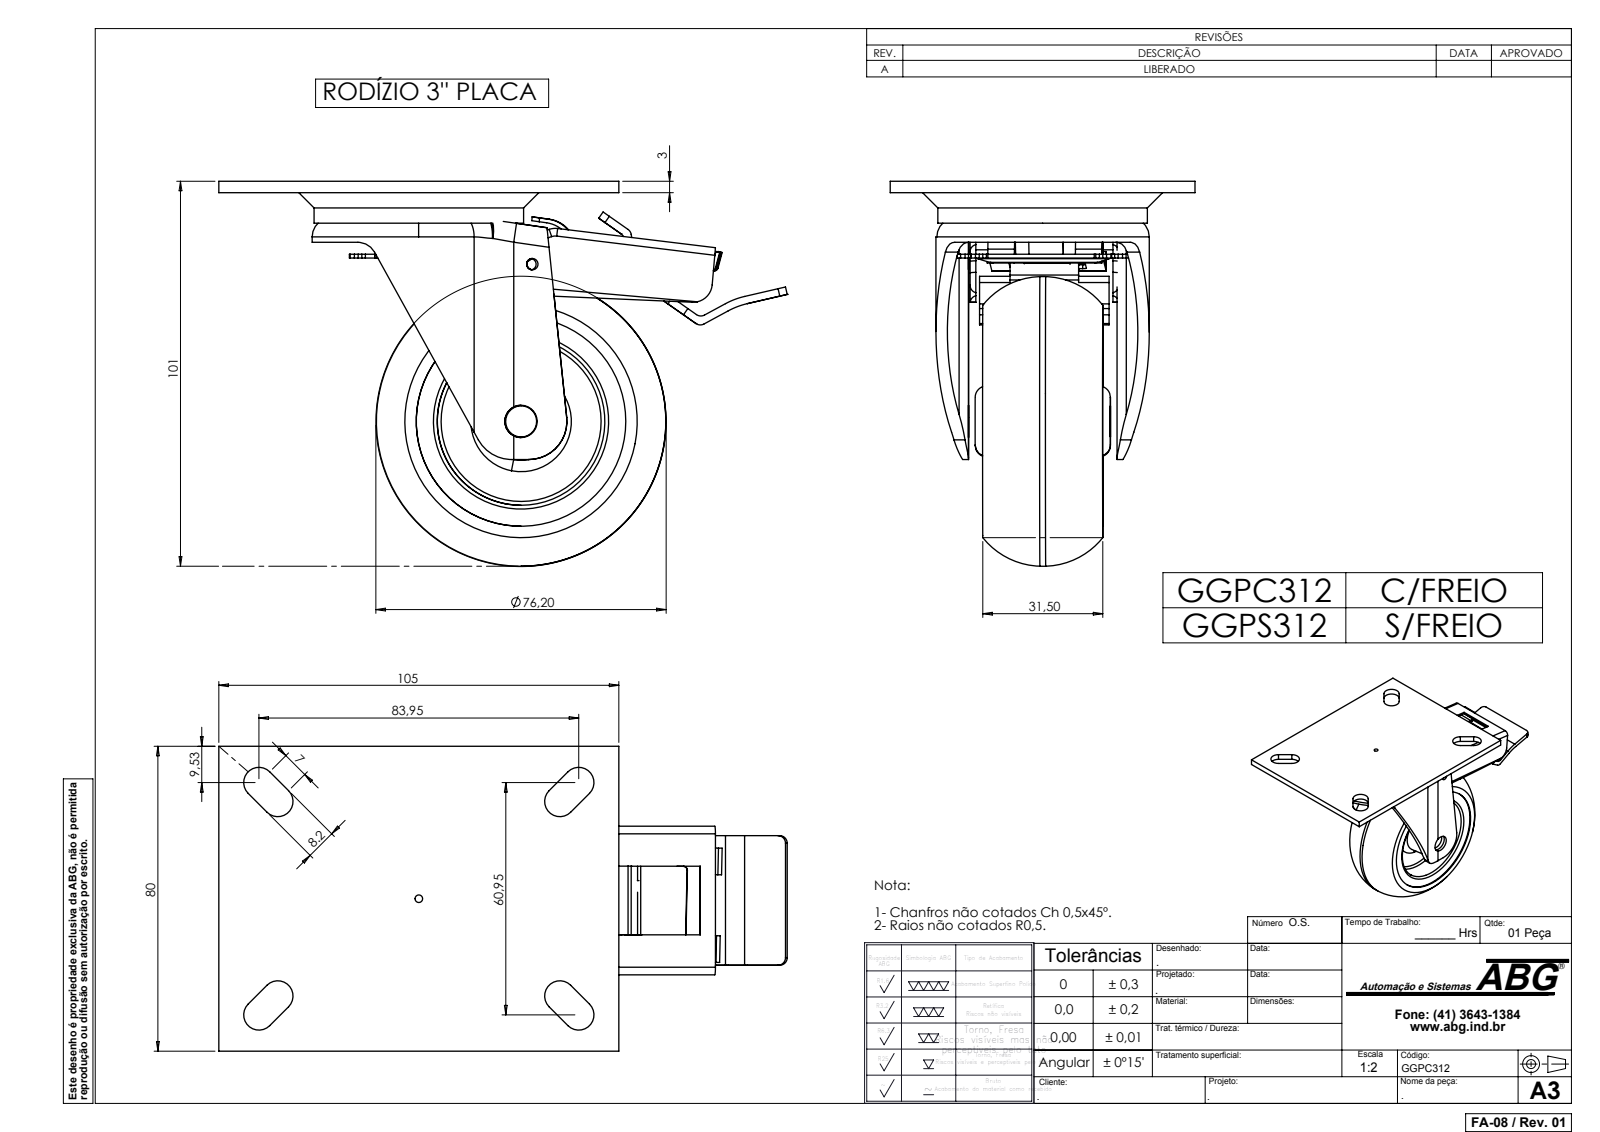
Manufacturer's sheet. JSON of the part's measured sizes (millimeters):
{"part_name": "ROD 3'''''''' -1; ROD 3'''''''' -3-1; GGPCF312; ROD 3''''''''-4 (+3 more)", "step_written_by": "SolidWorks 2007 (CONFIG_CONTROL_DESIGN)", "units": "millimeters", "bodies": {"solids": 6, "faces": 371, "planar": 152, "cylindrical": 176, "other": 43}, "overall_size": [149.2, 101.01, 80], "volume_mm3": 162965, "surface_area_mm2": 65323, "round_holes": [[3, 2], [8.5, 2], [44, 2], [55, 2], [2, 1], [8.2, 1], [25, 1], [50, 1]], "round_bosses_or_shafts": [[76, 1], [55, 1]], "partial_cylinders_radius": [[0.7, 32], [2, 25], [4, 20], [1, 14], [5, 8], [20, 6], [6, 2], [8, 2]], "face_to_face_distances": [3, 8, 1.5, 11, 1, 15.75, 23.25, 39, 19, 4.25], "hole_center_spacings": [41.37]}
